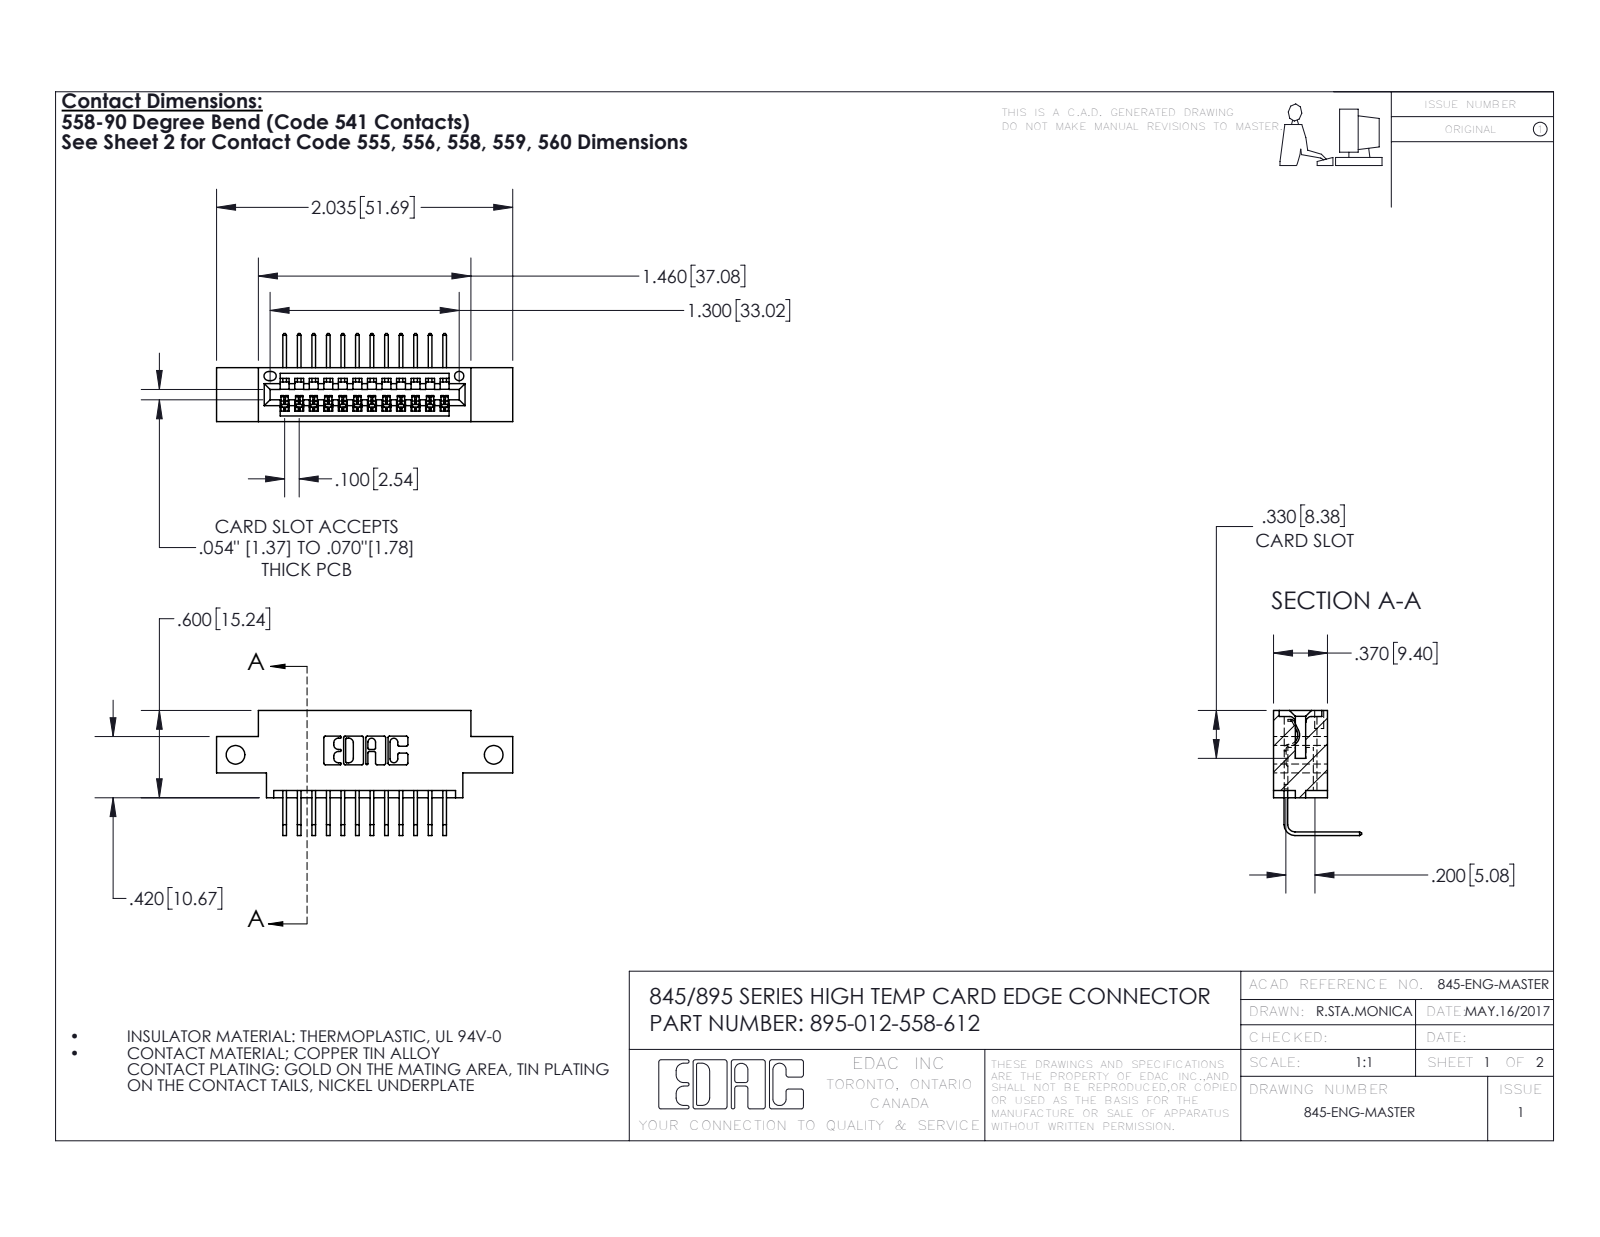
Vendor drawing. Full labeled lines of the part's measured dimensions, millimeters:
Part name (STEP PRODUCT): 345-292-001_558 Tail - 2; 395-012-558-612; 345 Part_0.170 Offset - Side Mount
STEP written by: SolidWorks 2016 (CONFIG_CONTROL_DESIGN)
Units: millimetres
Bodies: 13 solids, 850 faces (588 planar, 262 cylindrical, 0 other)
Overall size (bounding box): 51.7 × 21.8 × 15.4
Volume: 4 510 mm³ · Surface area: 5 796 mm²
Round holes (diameter × count): ⌀3.3 ×2, ⌀1.6 ×1
Partial cylindrical surfaces — rounded edges, fillets, slot ends (radius × count): R0.2 ×24, R0.3 ×22, R0.2 ×6, R0.8 ×6, R0.7 ×3, R0.8 ×2, R1 ×2, R0.4 ×1
Main face-to-face distances: 9.4, 1.8, 7.6, 5.1, 2.5, 6.9, 0.6, 2.5, 5.7, 15.2
Hole centre spacings: 45.1
